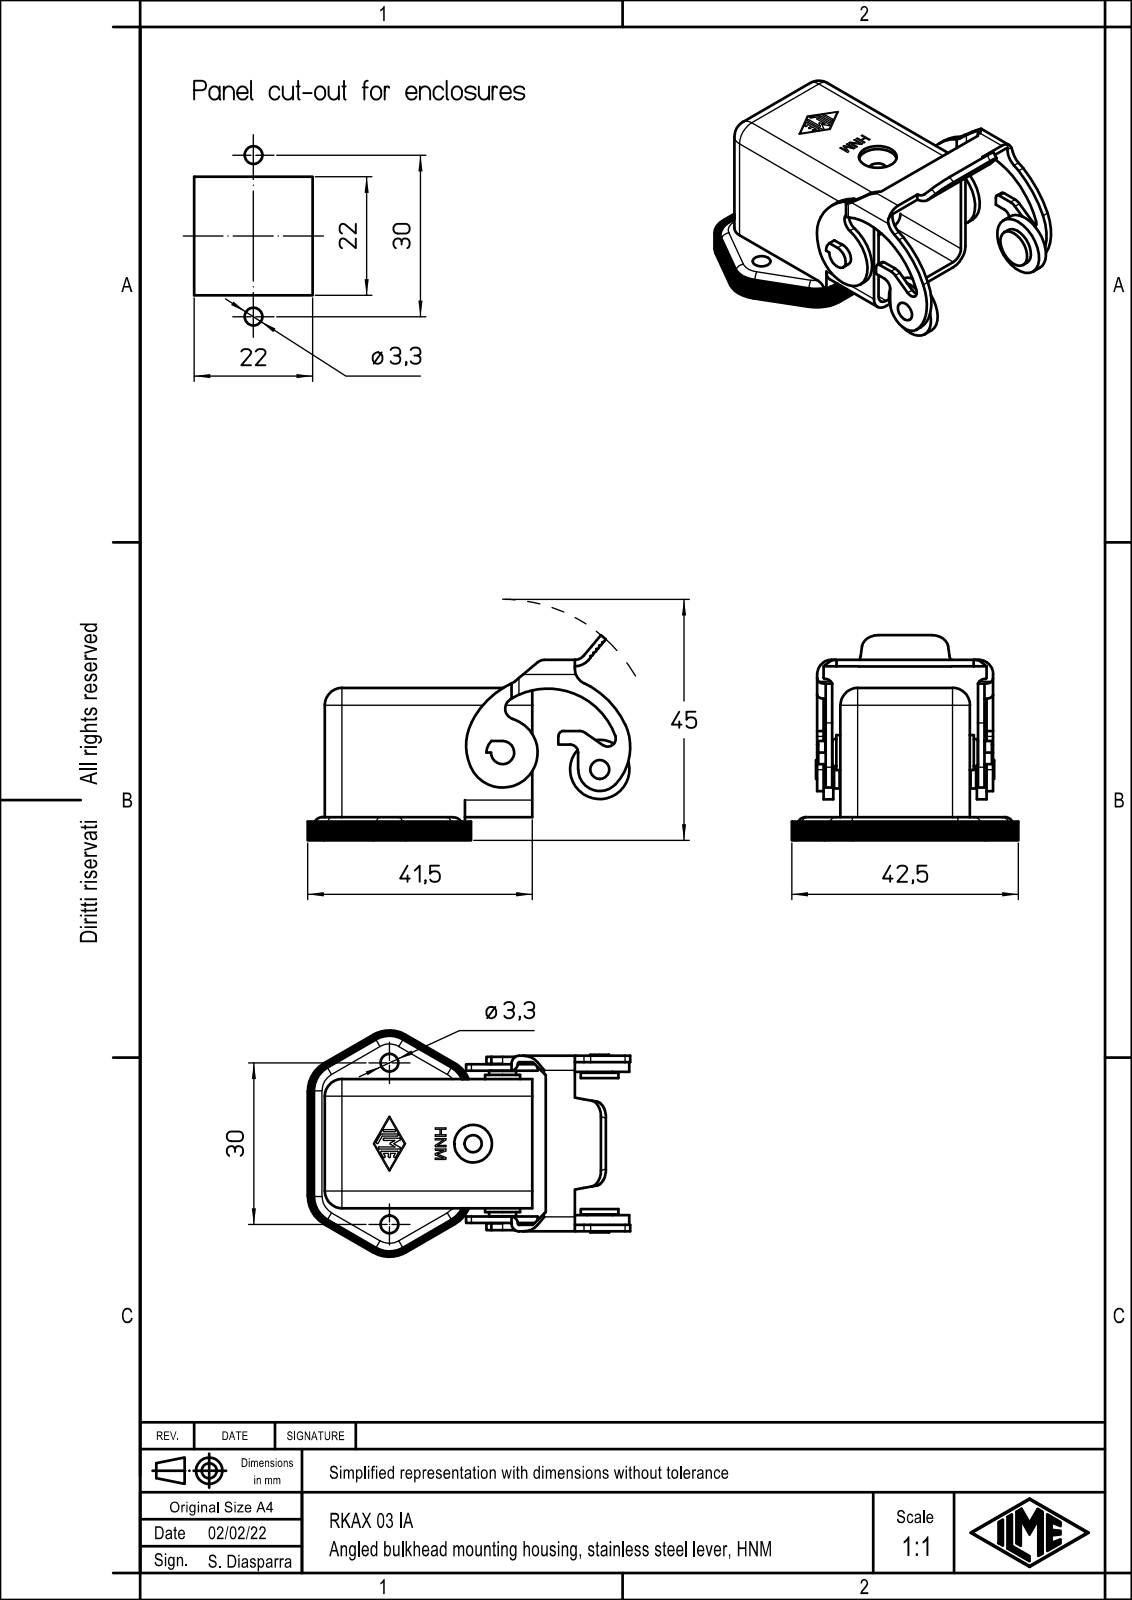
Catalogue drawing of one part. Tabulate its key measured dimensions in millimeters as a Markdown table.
| quantity | value |
| --- | --- |
| part name | RKAX_03_IA |
| STEP written by | Creo Elements/Direct Modeling 20.1B 02-Apr-2019 (C) Parametric Technology GmbH (AUTOMOTIVE_DESIGN) |
| units | millimeters |
| bodies | 1 solid, 317 faces (159 planar, 147 cylindrical, 11 other) |
| overall size | 59.81 × 42.02 × 38.1 |
| volume | 8 502 mm³ |
| surface area | 11 863 mm² |
| round holes (diameter × count) | 2.6 × 2, 3.3 × 2, 3.2 × 1, 7 × 1 |
| round bosses / shafts (diameter × count) | 11 × 1, 7 × 1, 6.5 × 1, 5 × 1, 4.8 × 1, 4.3 × 1, 3.5 × 1 |
| partial cylindrical surfaces (radius × count) | 2 × 14, 0.2 × 13, 5 × 12, 3.2 × 8, 1.5 × 7, 6 × 6, 3 × 5, 1.4 × 4 |
| main face-to-face distances | 1.2, 22.8, 24, 21.6, 28.3, 4.3, 27.1, 1.35, 28, 5.2 |
| hole center spacings | 21.57, 30 |
